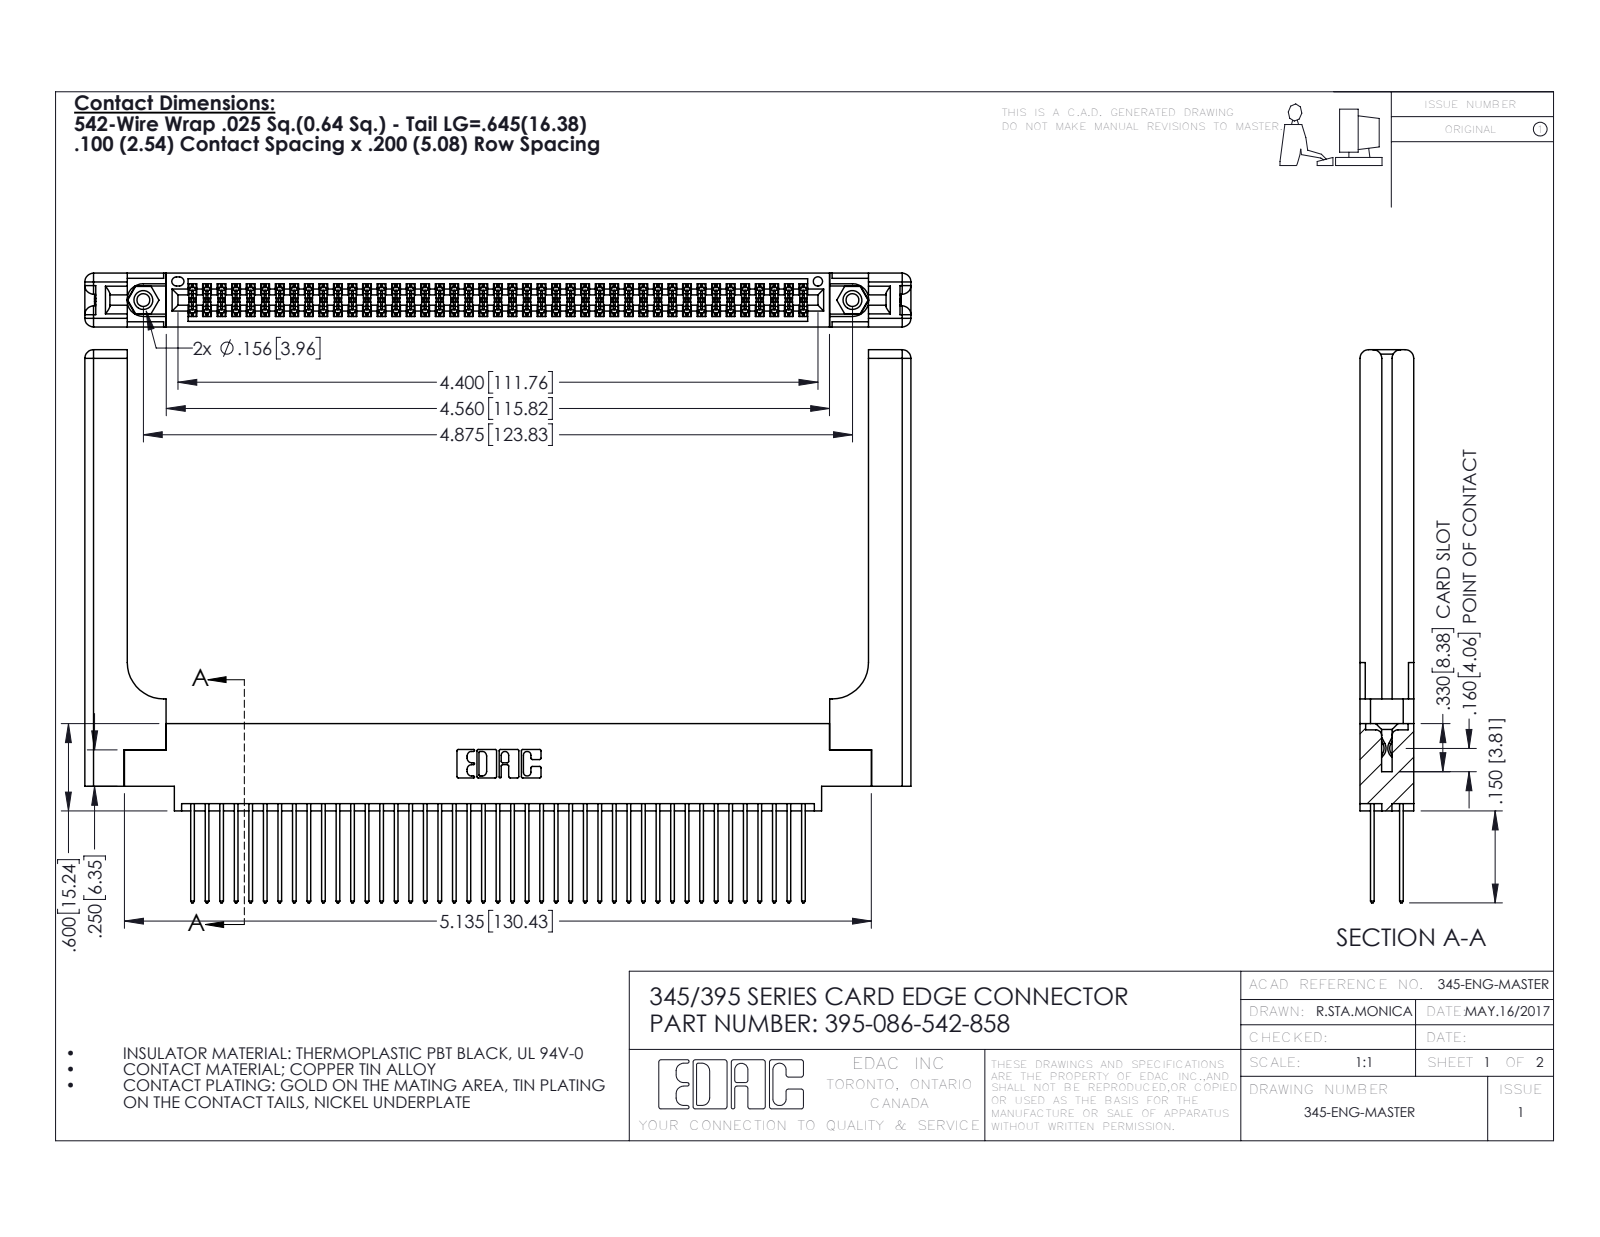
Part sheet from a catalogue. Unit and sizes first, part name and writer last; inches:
Units: inches
Overall size (bounding box): 5.679 × 3.802 × 0.37
Round holes (diameter × count): ⌀0.089 ×2, ⌀0.125 ×2, ⌀0.156 ×2, ⌀0.064 ×1
Round bosses / shafts (diameter × count): ⌀0.155 ×2
Partial cylindrical surfaces — rounded edges, fillets, slot ends (radius × count): R0.006 ×129, R0.01 ×86, R0.01 ×22, R0.06 ×16, R0.007 ×6, R0.031 ×6, R0.026 ×3, R0.014 ×2
Main face-to-face distances: 0.072, 0.298, 0.37, 0.098, 0.272, 0.025, 0.2, 0.225, 0.175, 0.148
Hole centre spacings: 0.27, 4.639, 4.875
Volume: 1.39 in³ · Surface area: 43.78 in²
Bodies: 91 solids, 4686 faces (3070 planar, 1556 cylindrical, 60 other)
Part name (STEP PRODUCT): 345-292-001_345-293-142; 345-220-058_345-220-058; 345-250-001_345-250-001-102; 345 Part_0.170 Offset - 0.156 Dia-TH (+1 more)
STEP written by: SolidWorks 2016 (CONFIG_CONTROL_DESIGN)
